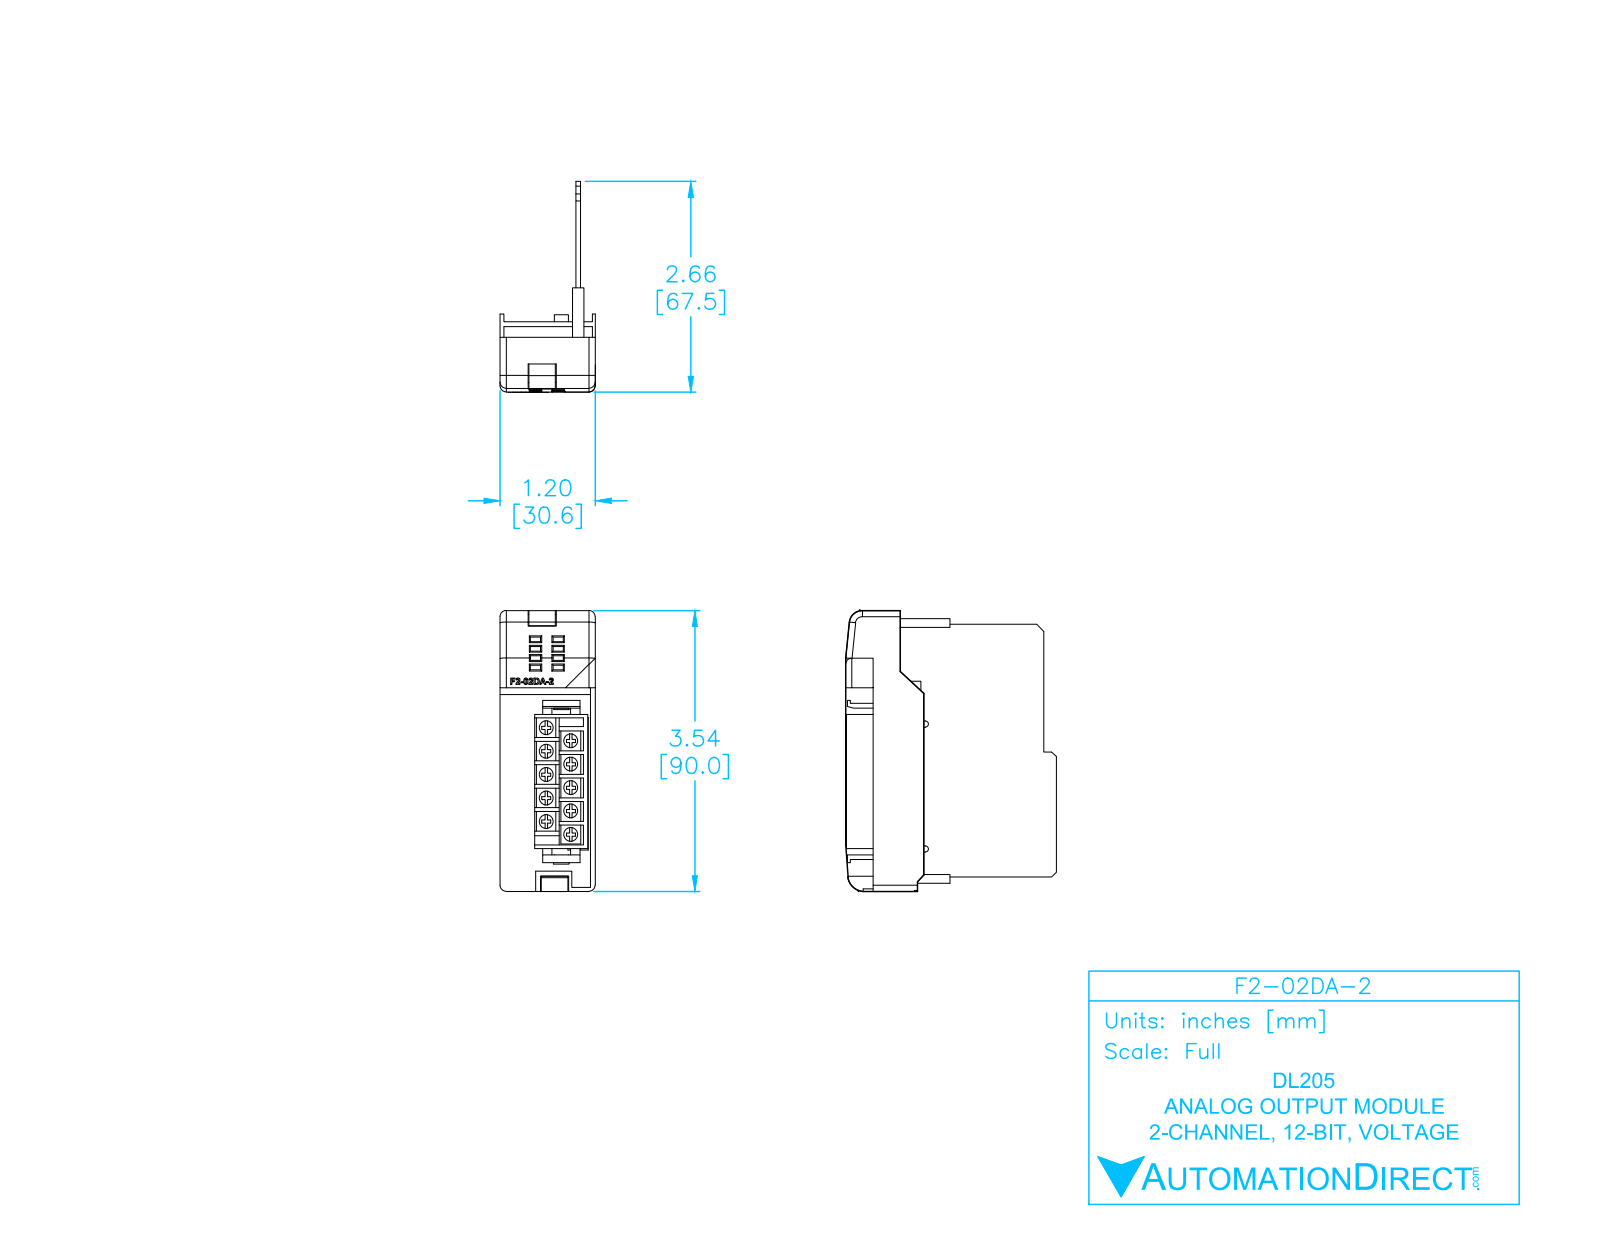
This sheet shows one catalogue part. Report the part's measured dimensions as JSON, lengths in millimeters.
{"part_name": "F2-02DA-2_ModuleCase_light_NEW", "step_written_by": "SolidWorks 2009 (AUTOMOTIVE_DESIGN)", "units": "millimeters", "bodies": {"solids": 6, "faces": 580, "planar": 413, "cylindrical": 75, "other": 92}, "overall_size": [90, 67.61, 30.55], "volume_mm3": 25374, "surface_area_mm2": 28533, "round_bosses_or_shafts": [[4.5, 10]], "partial_cylinders_radius": [[0.35, 16], [2, 9], [0.25, 2], [1, 2], [1.25, 2], [4.12, 1], [5.39, 1]], "face_to_face_distances": [1.5, 4.72, 6.22, 2.37, 3.87, 2.35, 3.22, 0.85, 8.14, 24.28]}
